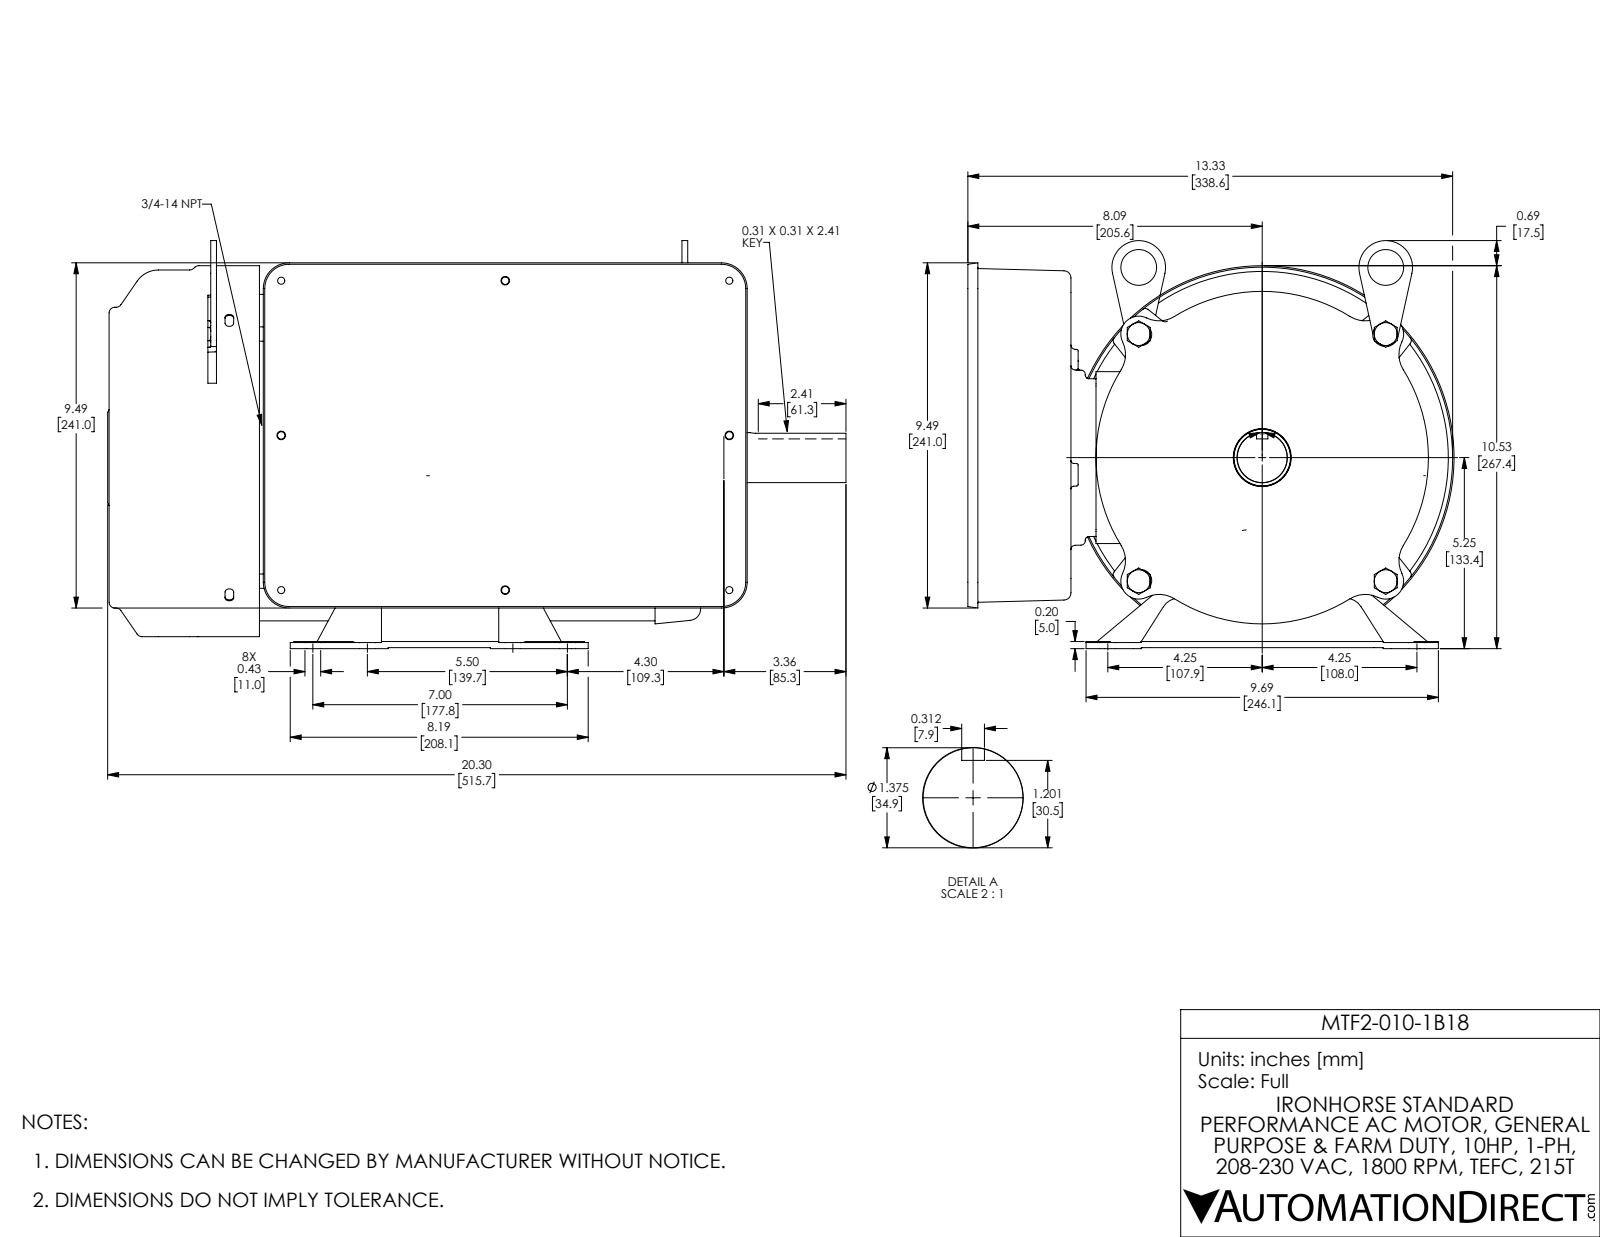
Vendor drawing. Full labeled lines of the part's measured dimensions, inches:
Part name (STEP PRODUCT): MTF2-010-1B18
STEP written by: SolidWorks 2017 (AUTOMOTIVE_DESIGN)
Units: inches
Bodies: 24 solids, 3480 faces (1086 planar, 847 cylindrical, 1547 other)
Overall size (bounding box): 20.303 × 13.37 × 11.216
Volume: 250.4 in³ · Surface area: 2 602 in²
Round holes (diameter × count): ⌀0.205 ×9, ⌀0.236 ×9, ⌀0.433 ×8, ⌀0.197 ×7, ⌀0.472 ×5, ⌀0.458 ×4, ⌀0.402 ×3, ⌀0.28 ×2, ⌀0.354 ×2, ⌀0.906 ×2, ⌀0.984 ×2, ⌀0.315 ×1
Round bosses / shafts (diameter × count): ⌀0.394 ×4, ⌀0.33 ×4, ⌀0.606 ×3, ⌀0.445 ×2, ⌀10.551 ×1, ⌀10.315 ×1, ⌀8.974 ×1, ⌀8.268 ×1
Partial cylindrical surfaces — rounded edges, fillets, slot ends (radius × count): R0.039 ×48, R0.079 ×38, R0.118 ×31, R0.197 ×30, R0.059 ×18, R0.02 ×16, R0.156 ×9, R0.591 ×8
Main face-to-face distances: 0.039, 0.197, 2.835, 2.795, 2.638, 2.598, 0.163, 2.559, 0.689, 0.886
Hole centre spacings: 3.398, 7.676, 6.793, 10.502, 1.5, 3.15, 3.488, 4.252
